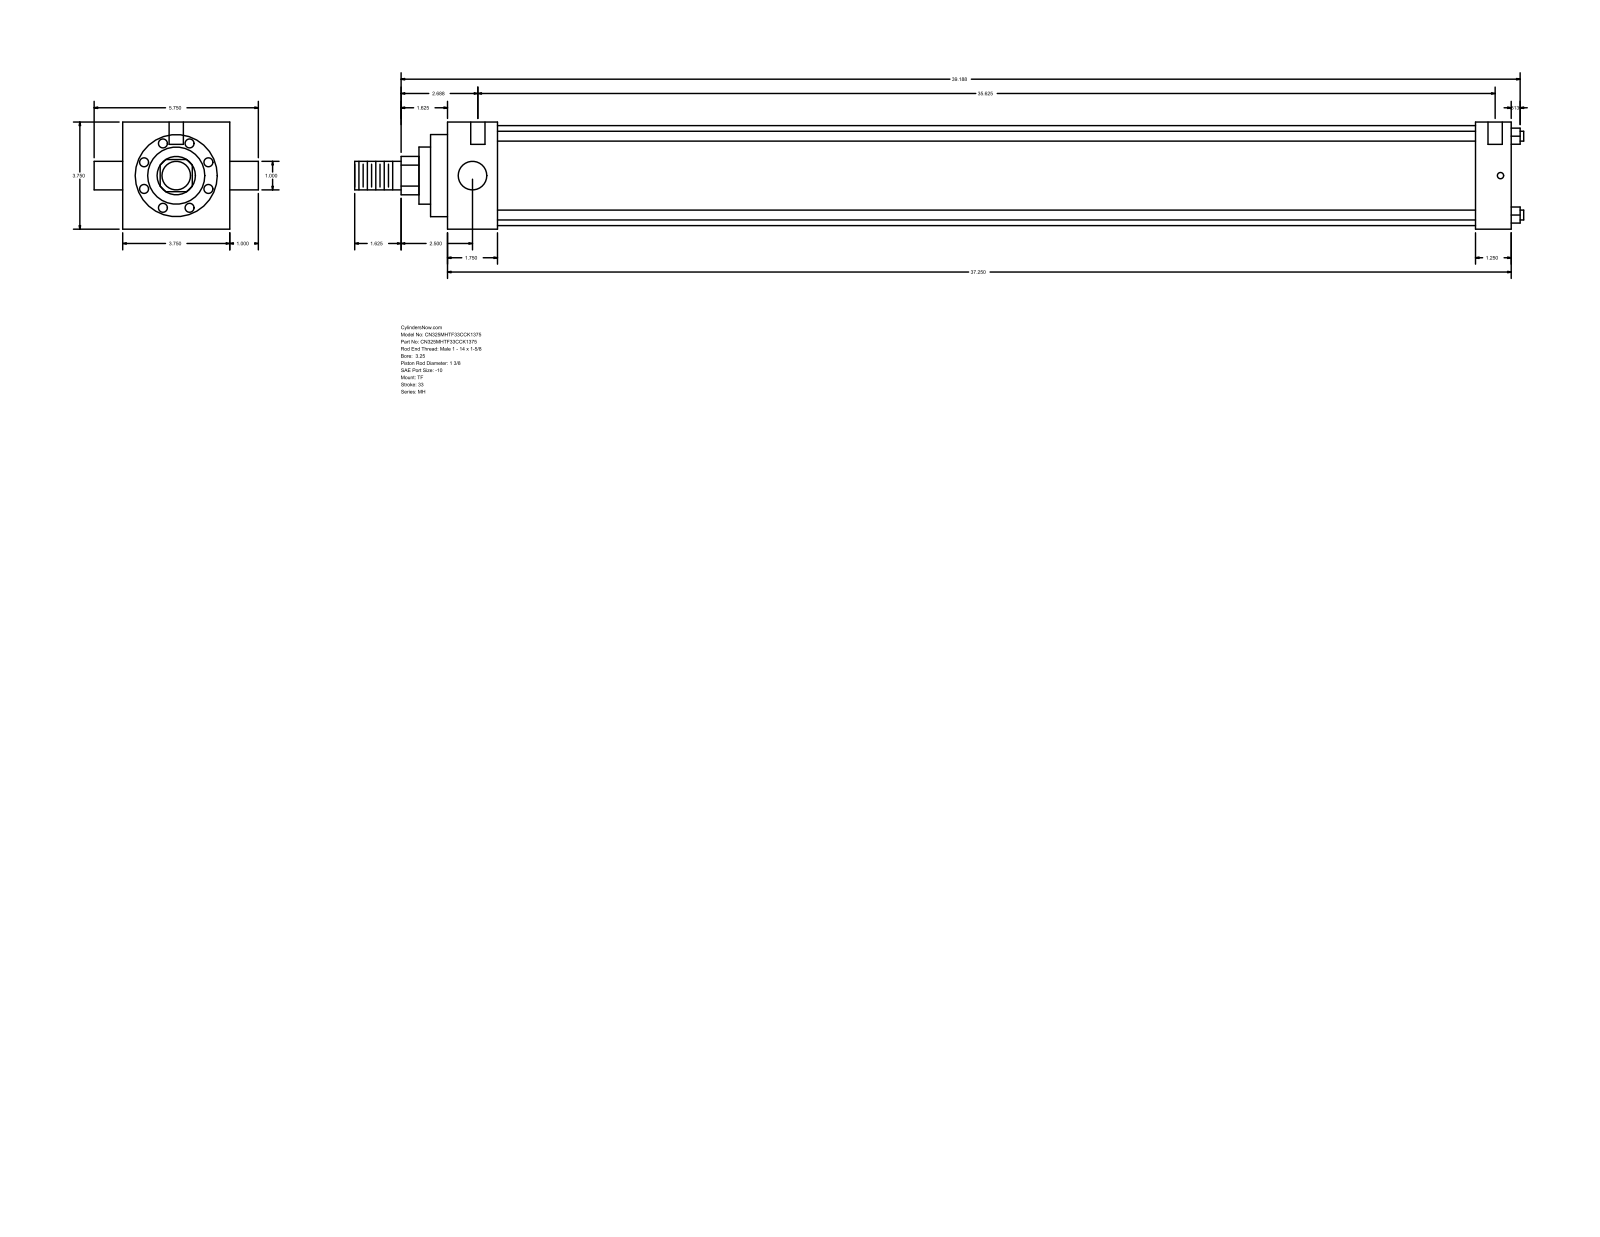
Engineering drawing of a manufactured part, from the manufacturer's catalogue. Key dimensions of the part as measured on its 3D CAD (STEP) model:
Part name (STEP PRODUCT): MH_TF__0325_1.375
STEP written by: GSSL Pune (CONFIG_CONTROL_DESIGN)
Units: millimetres
Bodies: 0 solids, 86 faces (61 planar, 25 cylindrical, 0 other)
Overall size (bounding box): 1039.81 × 146.05 × 95.25
Round holes (diameter × count): ⌀5.56 ×3, ⌀12.7 ×2
Round bosses / shafts (diameter × count): ⌀8.76 ×4, ⌀25.4 ×2, ⌀88.9 ×1, ⌀73.03 ×1, ⌀50.8 ×1, ⌀34.92 ×1
Partial cylindrical surfaces — rounded edges, fillets, slot ends (radius × count): R17.06 ×1
Main face-to-face distances: 95.24, 946.15, 44.45, 914.4, 869.95, 901.7, 31.75, 15.08, 59.53, 929.48
Hole centre spacings: 1.59, 4.76, 904.88, 906.47, 909.64, 911.23
